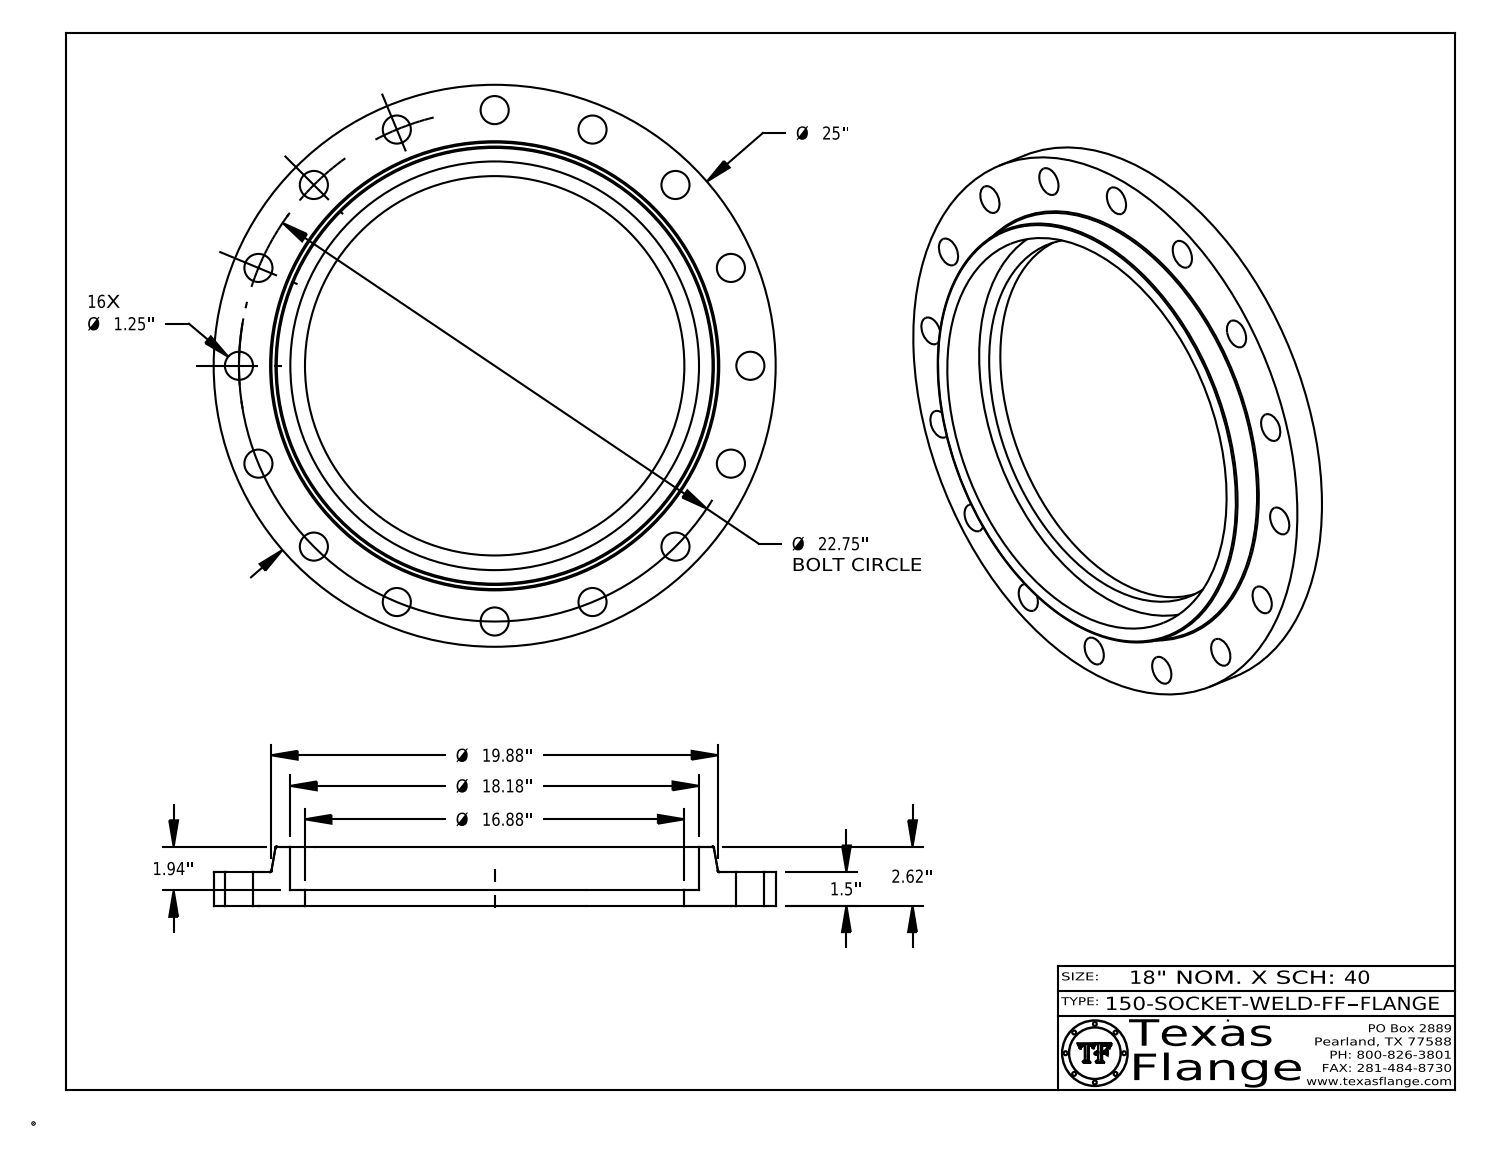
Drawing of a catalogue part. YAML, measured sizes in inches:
part_name: "150-SOCKET-WELD-FF"
step_written_by: "CATIA V5 STEP AP214 (AUTOMOTIVE_DESIGN)"
units: inches
bodies: {solids: 1, faces: 434, planar: 370, cylindrical: 58, other: 6}
overall_size: [25, 25, 2.62]
volume: 391.9
surface_area: 910.1
round_holes:
  - {diameter: 1.25, count: 16}
  - {diameter: 0.495, count: 1}
  - {diameter: 16.876, count: 1}
  - {diameter: 18.18, count: 1}
round_bosses_or_shafts:
  - {diameter: 0.03, count: 8}
  - {diameter: 25, count: 1}
  - {diameter: 0.39, count: 1}
face_to_face_distances: [1.5, 0.68, 0.82, 2.62, 1.94, 1.12, 1.485, 0.805, 0.015, 1.135]
hole_center_spacings: [12.639, 22.313, 11.375, 8.706, 16.087, 21.019, 4.438, 4.439]
